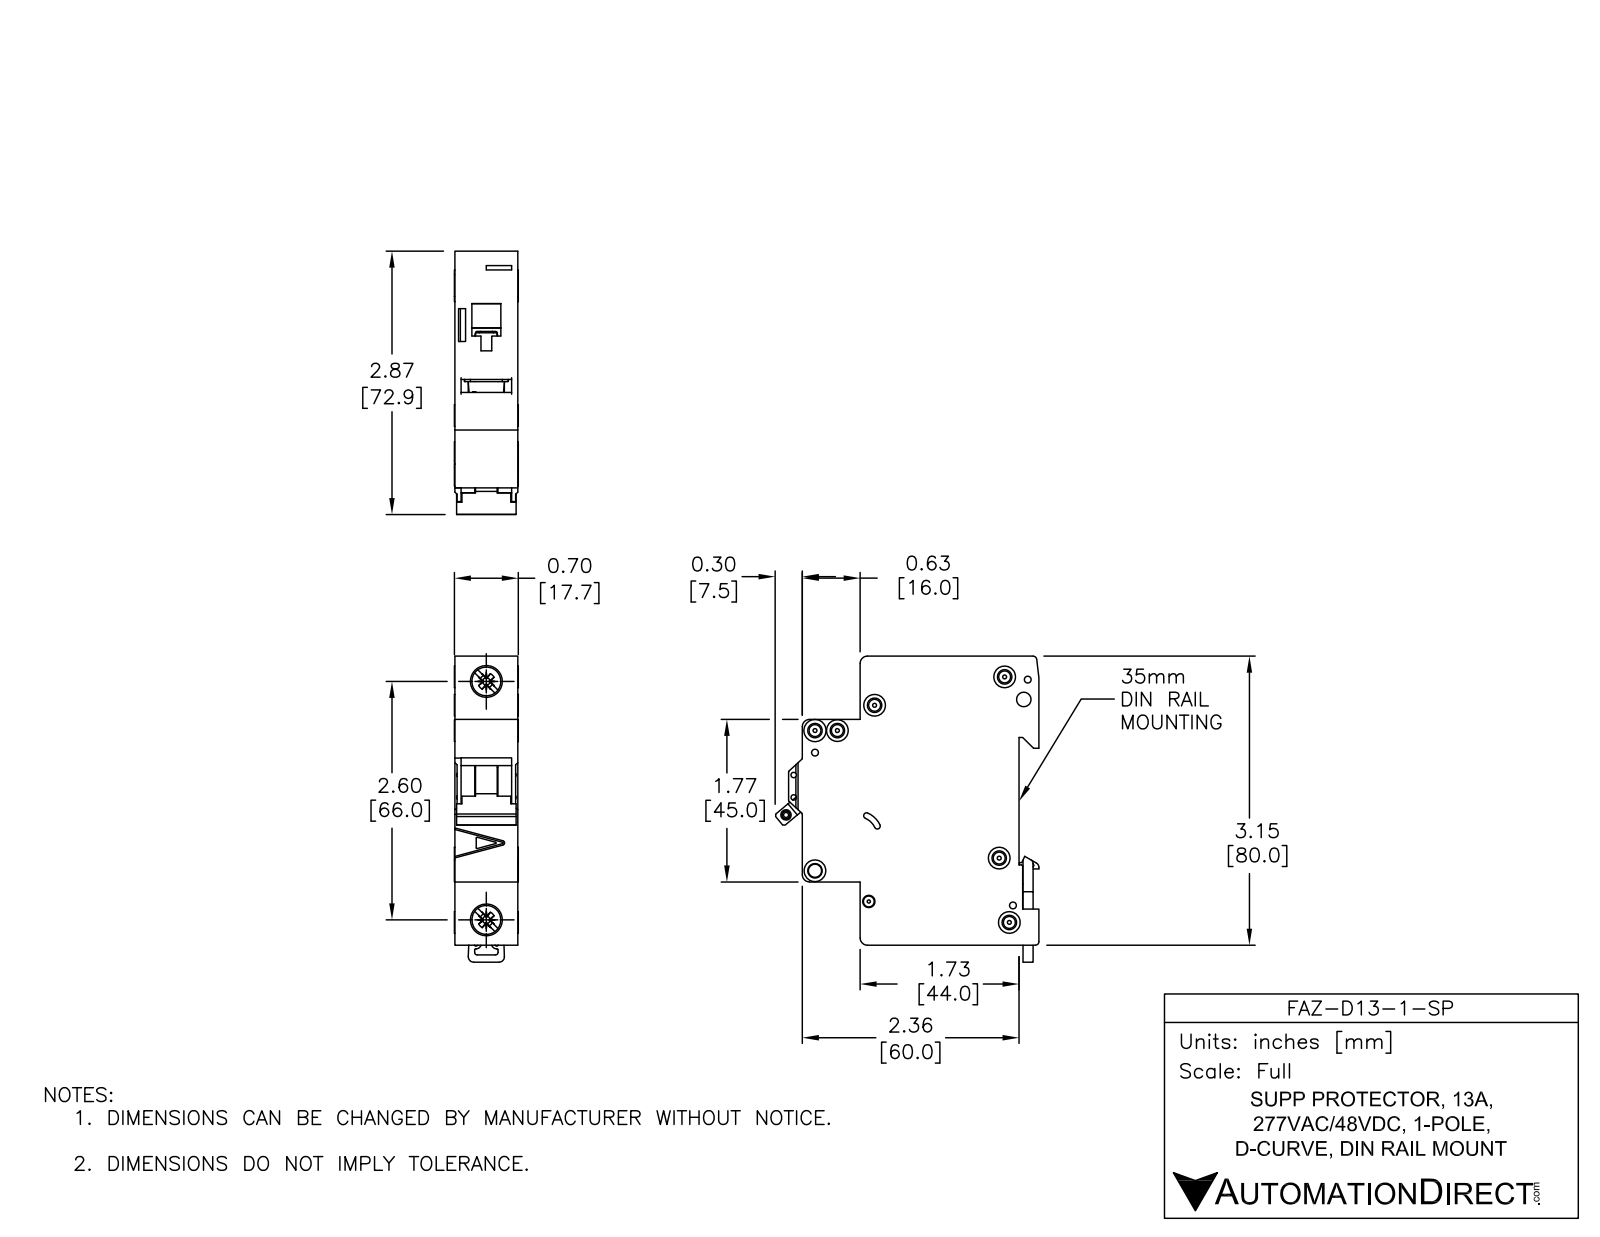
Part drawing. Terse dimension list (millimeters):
name: FAZ-D13-1-SP
written by: SolidWorks 2014 (AUTOMOTIVE_DESIGN)
unit: mm
bodies: 5 solids, 558 faces (235 planar, 202 cylindrical, 121 other)
size: 84.78 × 73.04 × 17.7
volume: 74 935 mm³; area: 19 545 mm²
holes: 6× ⌀3.6, 3× ⌀1.9, 2× ⌀1.09, 2× ⌀1.5, 2× ⌀4, 2× ⌀7.15, 1× ⌀2.15, 1× ⌀2.2, 1× ⌀2.55, 1× ⌀3.3, 1× ⌀3.4
bosses: 4× ⌀6, 2× ⌀8.2, 1× ⌀2.5
rounds: 30× R0.25, 13× R0.5, 8× R2, 5× R0.2, 4× R1, 2× R0.8, 2× R3, 1× R1.5
face distances: 17.5, 79.48, 5.5, 49.5, 44, 65.5, 60, 16, 1.75, 15.75
hole spacings: 6.2, 13.64, 4.81, 5.19, 5.61, 6.1, 6.44, 8.19
